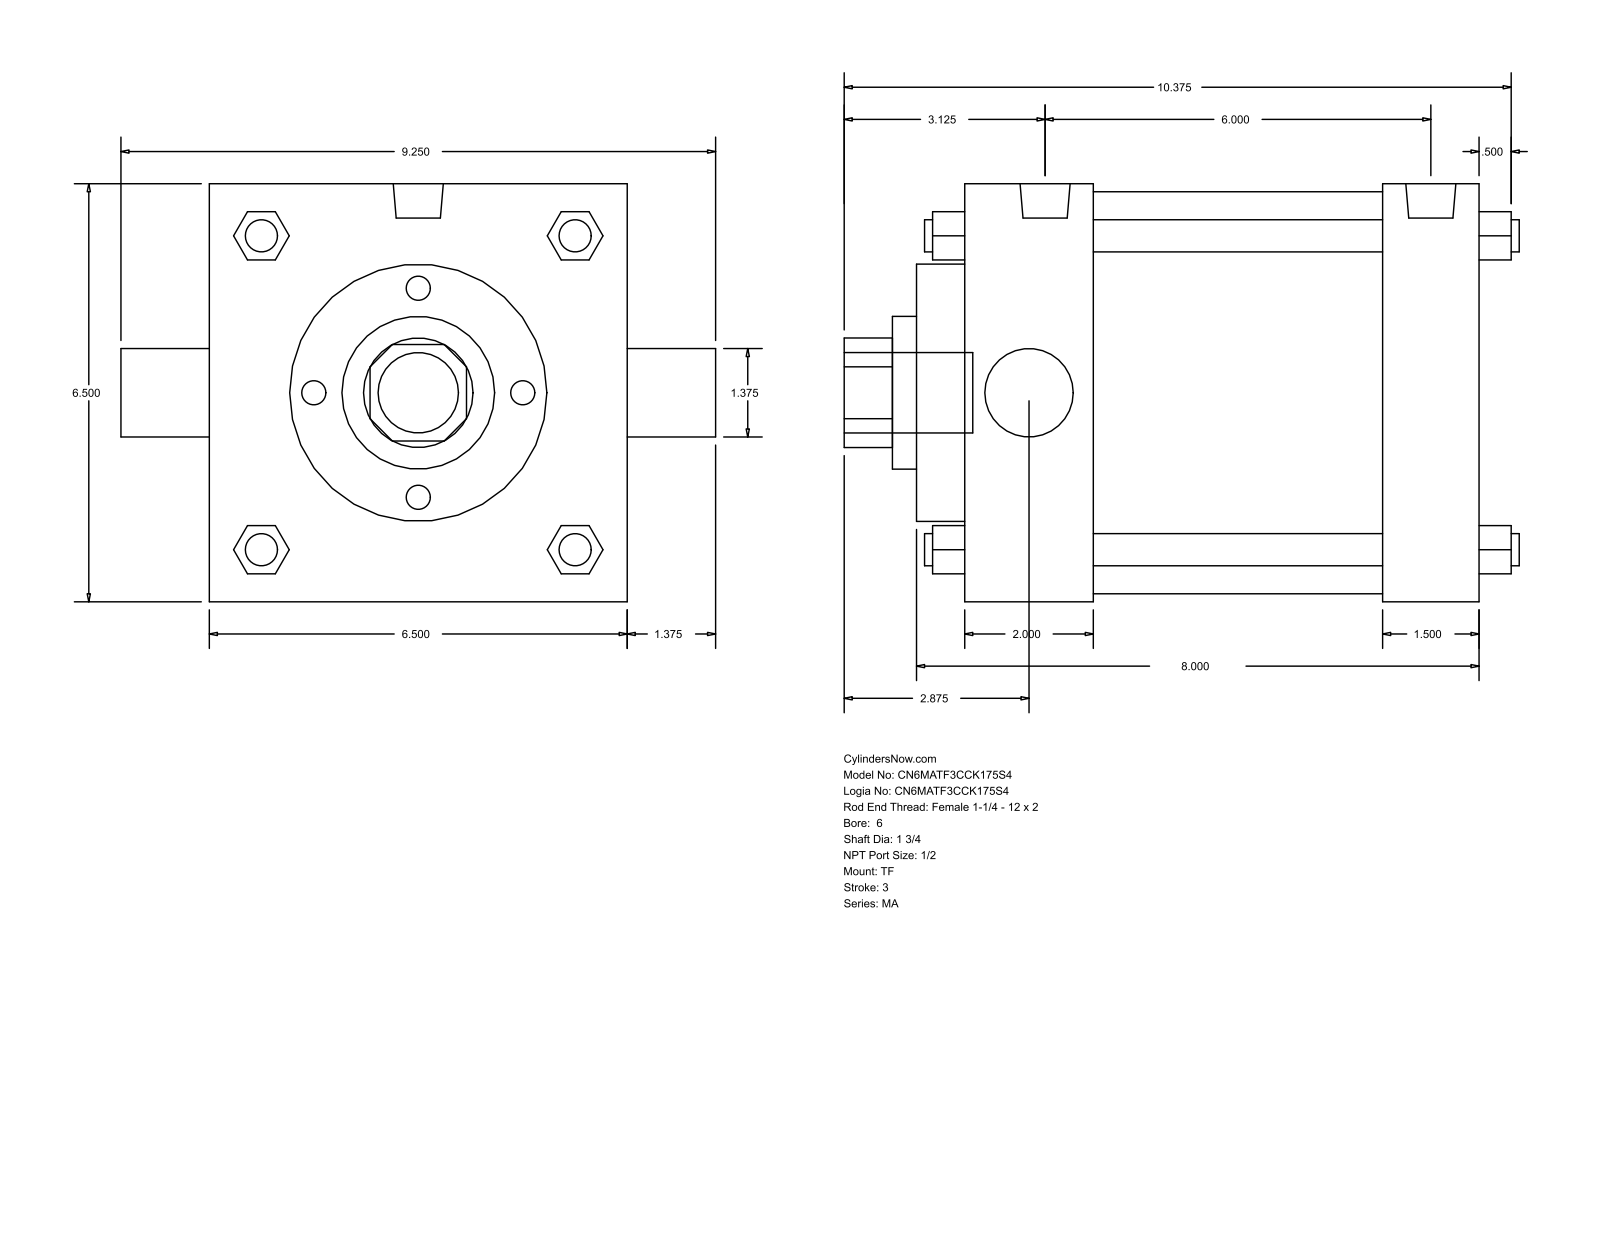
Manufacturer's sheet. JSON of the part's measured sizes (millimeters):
{"part_name": "MA_TF__0600_1.75", "step_written_by": "GSSL Pune (CONFIG_CONTROL_DESIGN)", "units": "millimeters", "bodies": {"solids": 0, "faces": 122, "planar": 93, "cylindrical": 29, "other": 0}, "overall_size": [266.7, 234.95, 165.1], "round_holes": [[34.92, 1], [44.45, 1], [60.33, 1], [101.6, 1], [158.75, 1]], "round_bosses_or_shafts": [[12.7, 4], [17.46, 3], [19.77, 2], [31.75, 1]], "partial_cylinders_radius": [[21.63, 1]], "face_to_face_distances": [165.1, 203.2, 19.05, 50.8, 38.1, 152.4, 114.3, 69.85, 184.15, 222.25]}
